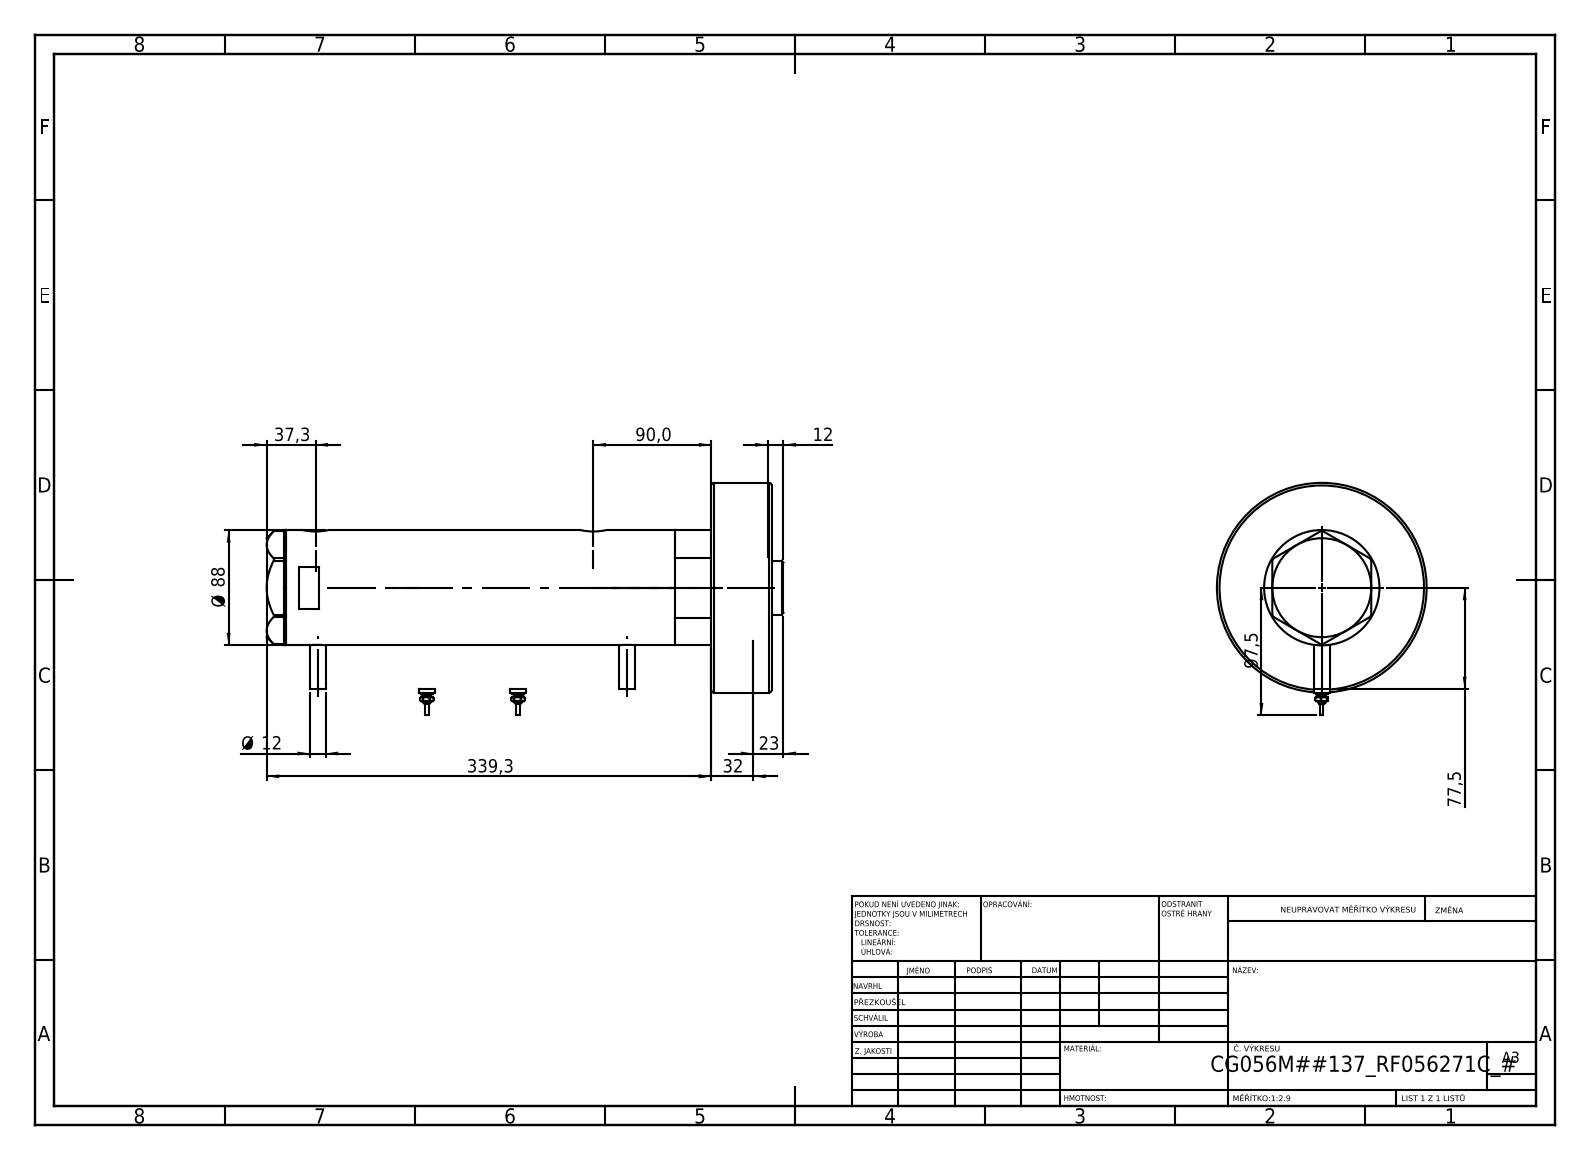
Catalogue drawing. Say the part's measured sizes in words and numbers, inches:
The part is named "V270CG_271C; V270CG_BACK; Switch; V270CG_FRONT (+2 more)". Its 3-D file was written by "SolidWorks 2019 (CONFIG_CONTROL_DESIGN)". It is 7 solids with 223 faces: 82 planar, 73 cylindrical and 68 other. Overall it measures 15.524 by 6.988 by 6.299 inches. Its volume is 169.4 cubic inches and its surface area 539.5 square inches. Round holes: 2 of diameter 0.492, 2 of diameter 0.518, 2 of diameter 0.787, 1 of diameter 0.571, 1 of diameter 1.654, 1 of diameter 1.713, 1 of diameter 2.205, 1 of diameter 2.362, 1 of diameter 2.953, 1 of diameter 3.15. Round bosses or shafts: 4 of diameter 0.472, 2 of diameter 0.354, 2 of diameter 0.276, 2 of diameter 0.177, 2 of diameter 0.098, 1 of diameter 6.299, 1 of diameter 3.465, 1 of diameter 2.874. The main face-to-face distances are 1.811, 12.768, 14.579, 9.228, 3.539, 5.35, 13.555, 1.024, 8.205, 11.744. The hole center spacings are 0.067, 1.016, 8.28, 8.346, 9.295, 9.362.
